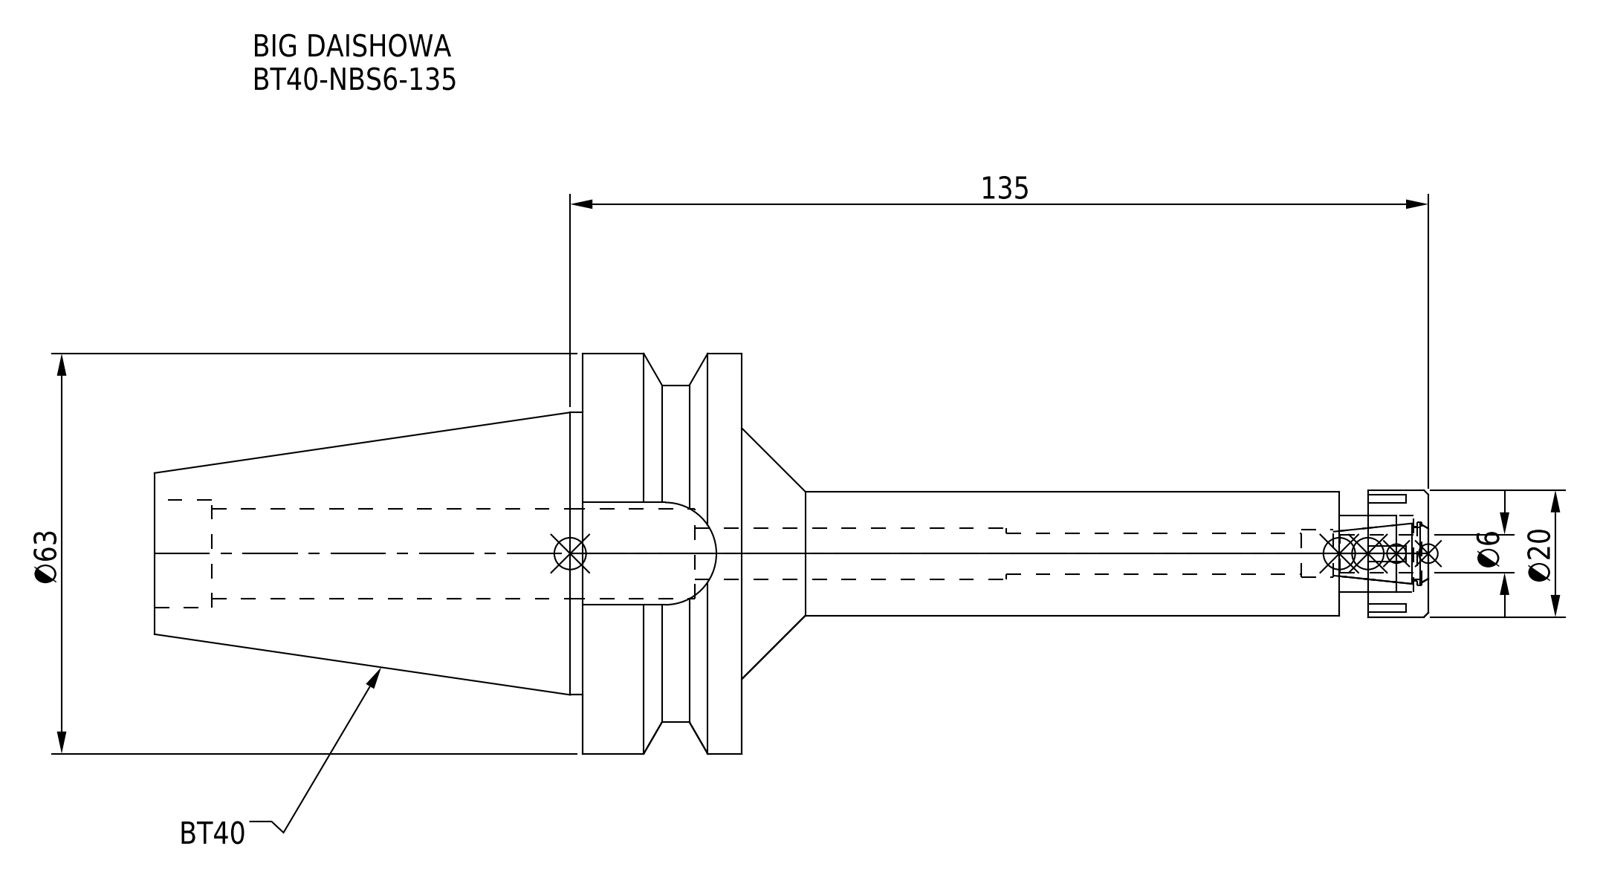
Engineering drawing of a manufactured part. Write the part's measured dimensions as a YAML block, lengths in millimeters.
part_name: "DXF_TEMP_ASSY_ASM_4_ASM.stp; NBN6_1.stp; BT40NB06135-060_ASM.stp; BT40-NBS6-135 (+3 more)"
step_written_by: "SolidWorks 2019 (CONFIG_CONTROL_DESIGN)"
units: millimeters
bodies: {solids: 2, faces: 93, planar: 45, cylindrical: 34, other: 14}
overall_size: [200.4, 63, 63]
volume: 150614
surface_area: 32491
round_holes:
  - {diameter: 6.4, count: 1}
  - {diameter: 7.5, count: 1}
  - {diameter: 8, count: 1}
  - {diameter: 8.5, count: 1}
  - {diameter: 10, count: 1}
  - {diameter: 12, count: 1}
  - {diameter: 14.2, count: 1}
  - {diameter: 17, count: 1}
round_bosses_or_shafts:
  - {diameter: 63, count: 1}
  - {diameter: 53, count: 1}
  - {diameter: 44.45, count: 1}
  - {diameter: 20, count: 1}
  - {diameter: 19.5, count: 1}
partial_cylinders:
  - {radius: 8.05, count: 1}
face_to_face_distances: [25, 45, 92.4, 67.4, 186.4, 4.5, 108, 133, 200.4, 14]
